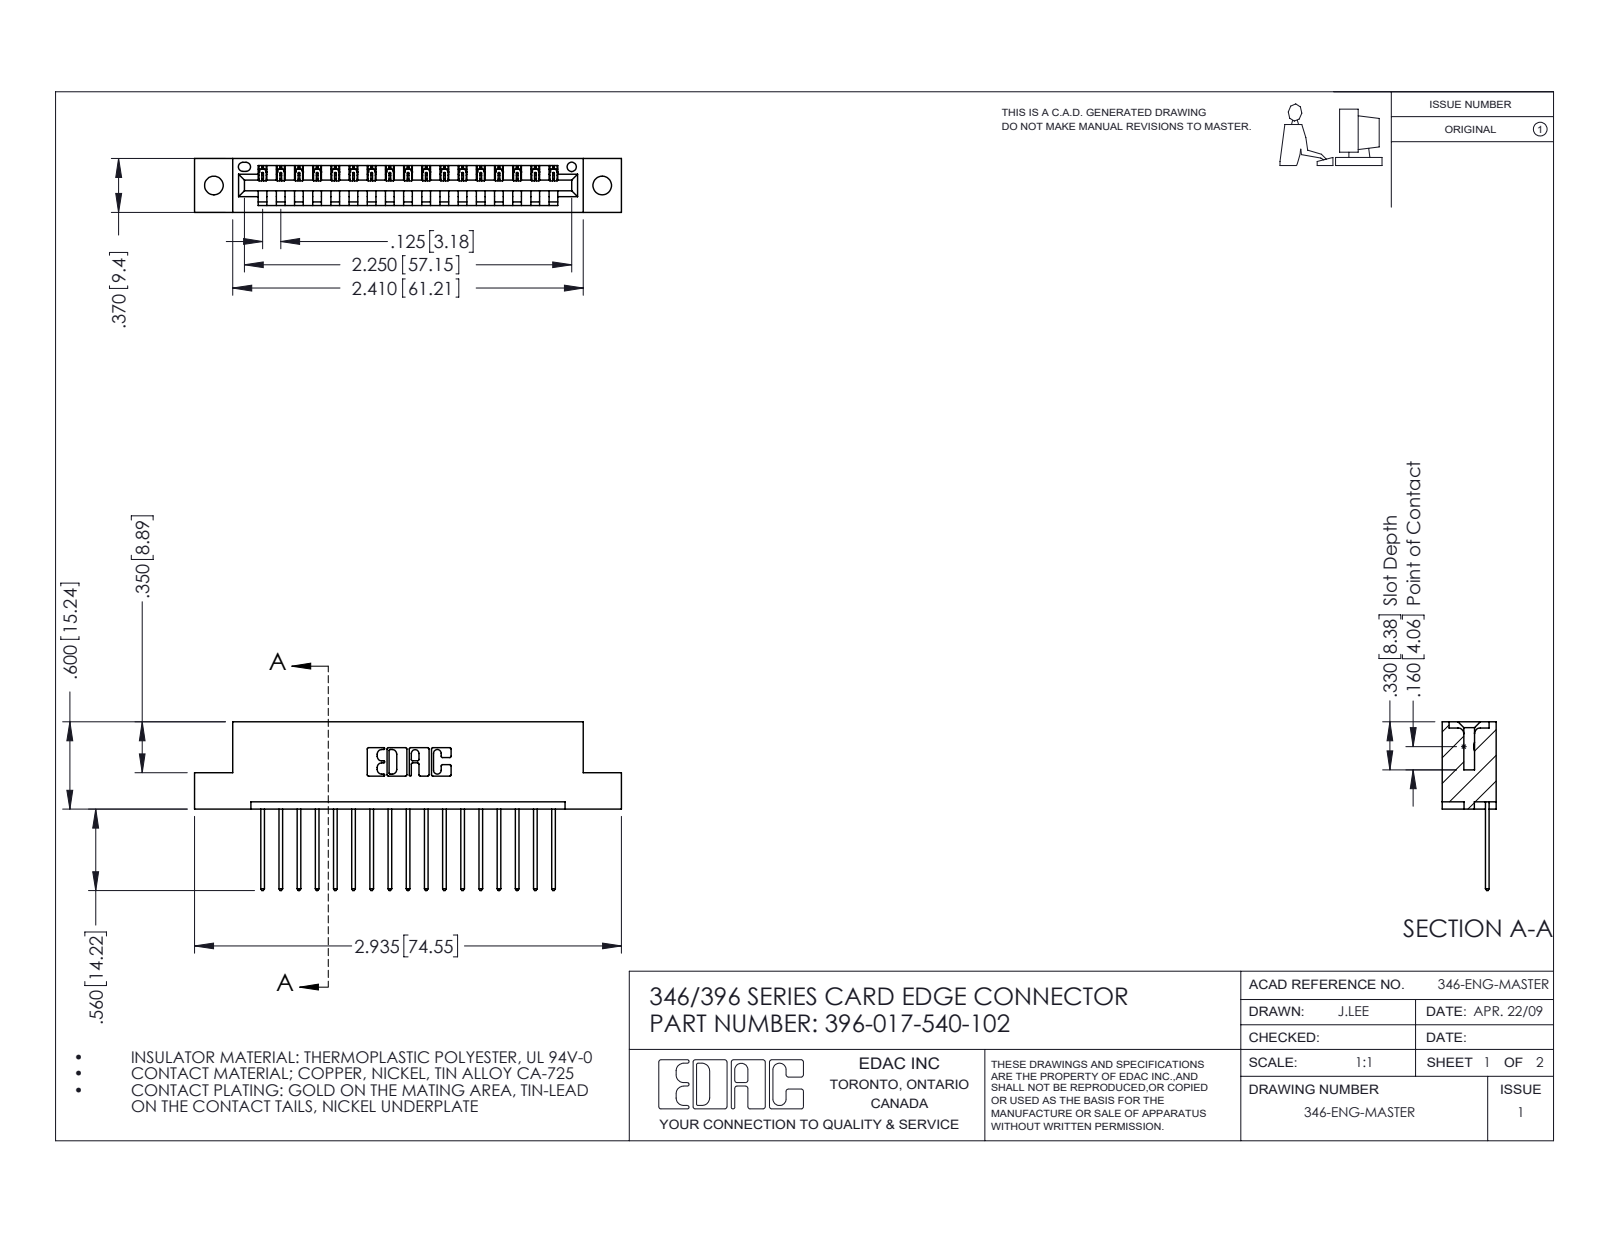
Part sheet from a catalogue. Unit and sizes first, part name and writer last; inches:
Units: inches
Overall size (bounding box): 2.935 × 1.16 × 0.37
Round holes (diameter × count): ⌀0.128 ×2, ⌀0.064 ×1
Partial cylindrical surfaces — rounded edges, fillets, slot ends (radius × count): R0.006 ×34, R0.01 ×34, R0.01 ×22, R0.007 ×6, R0.031 ×6, R0.026 ×3, R0.031 ×2, R0.04 ×2
Main face-to-face distances: 0.048, 0.322, 0.25, 0.37, 0.072, 0.298, 0.025, 0.148, 0.222, 0.1
Hole centre spacings: 0.246, 2.463, 2.67
Volume: 0.424 in³ · Surface area: 12.89 in²
Bodies: 18 solids, 1108 faces (756 planar, 352 cylindrical, 0 other)
Part name (STEP PRODUCT): 345-292-001_345-293-140; 346 Part_Flush Mounting Lugs - 0.128 Dia; 396-017-540-102
STEP written by: SolidWorks 2016 (CONFIG_CONTROL_DESIGN)
